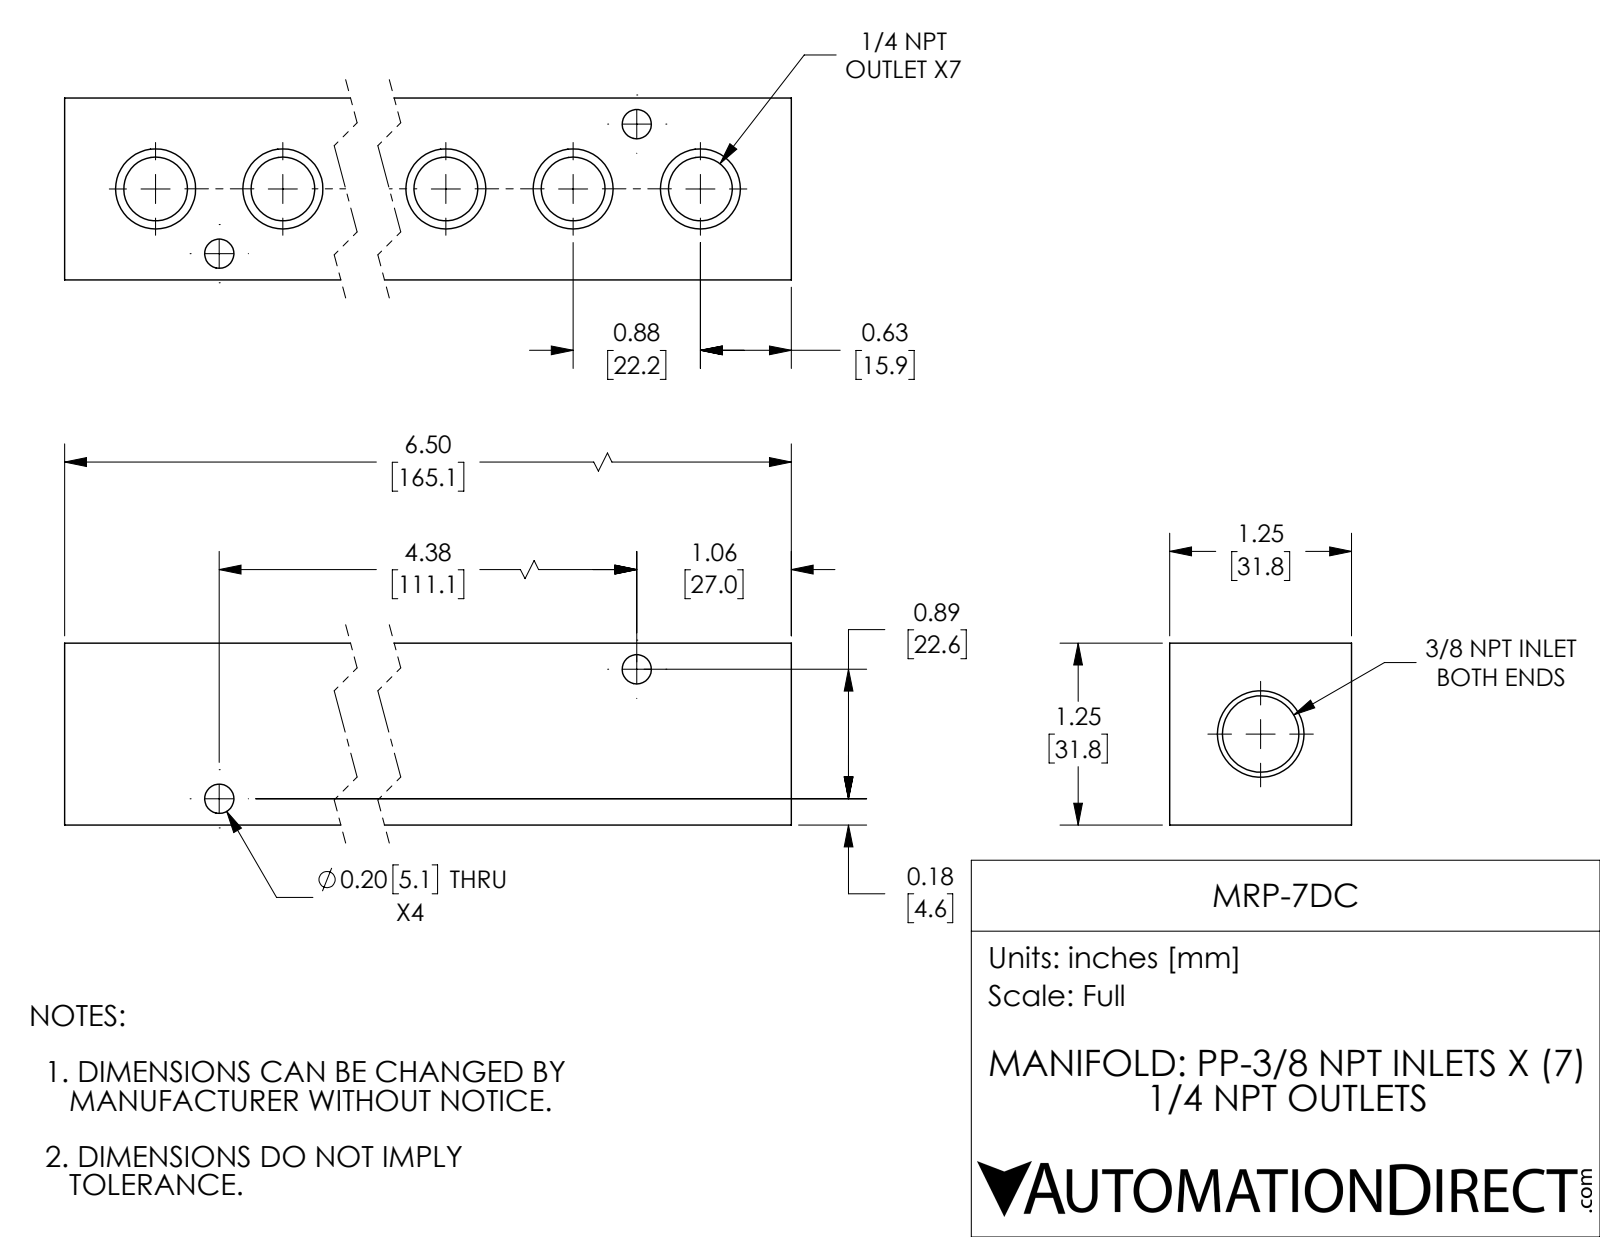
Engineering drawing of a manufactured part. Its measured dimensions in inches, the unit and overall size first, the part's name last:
Units: inches
Overall size (bounding box): 6.5 × 1.25 × 1.25
Round holes (diameter × count): ⌀0.438 ×7, ⌀0.201 ×4, ⌀0.525 ×1
Main face-to-face distances: 1.25, 6.5
Hole centre spacings: 0.624, 0.875, 1.75, 2.625, 0.875, 2.232, 3.5, 3.963
Volume: 8.174 in³ · Surface area: 49.92 in²
Bodies: 1 solid, 56 faces (6 planar, 32 cylindrical, 18 other)
Part name (STEP PRODUCT): MRP-7DC
STEP written by: SolidWorks 2018 (AUTOMOTIVE_DESIGN)
